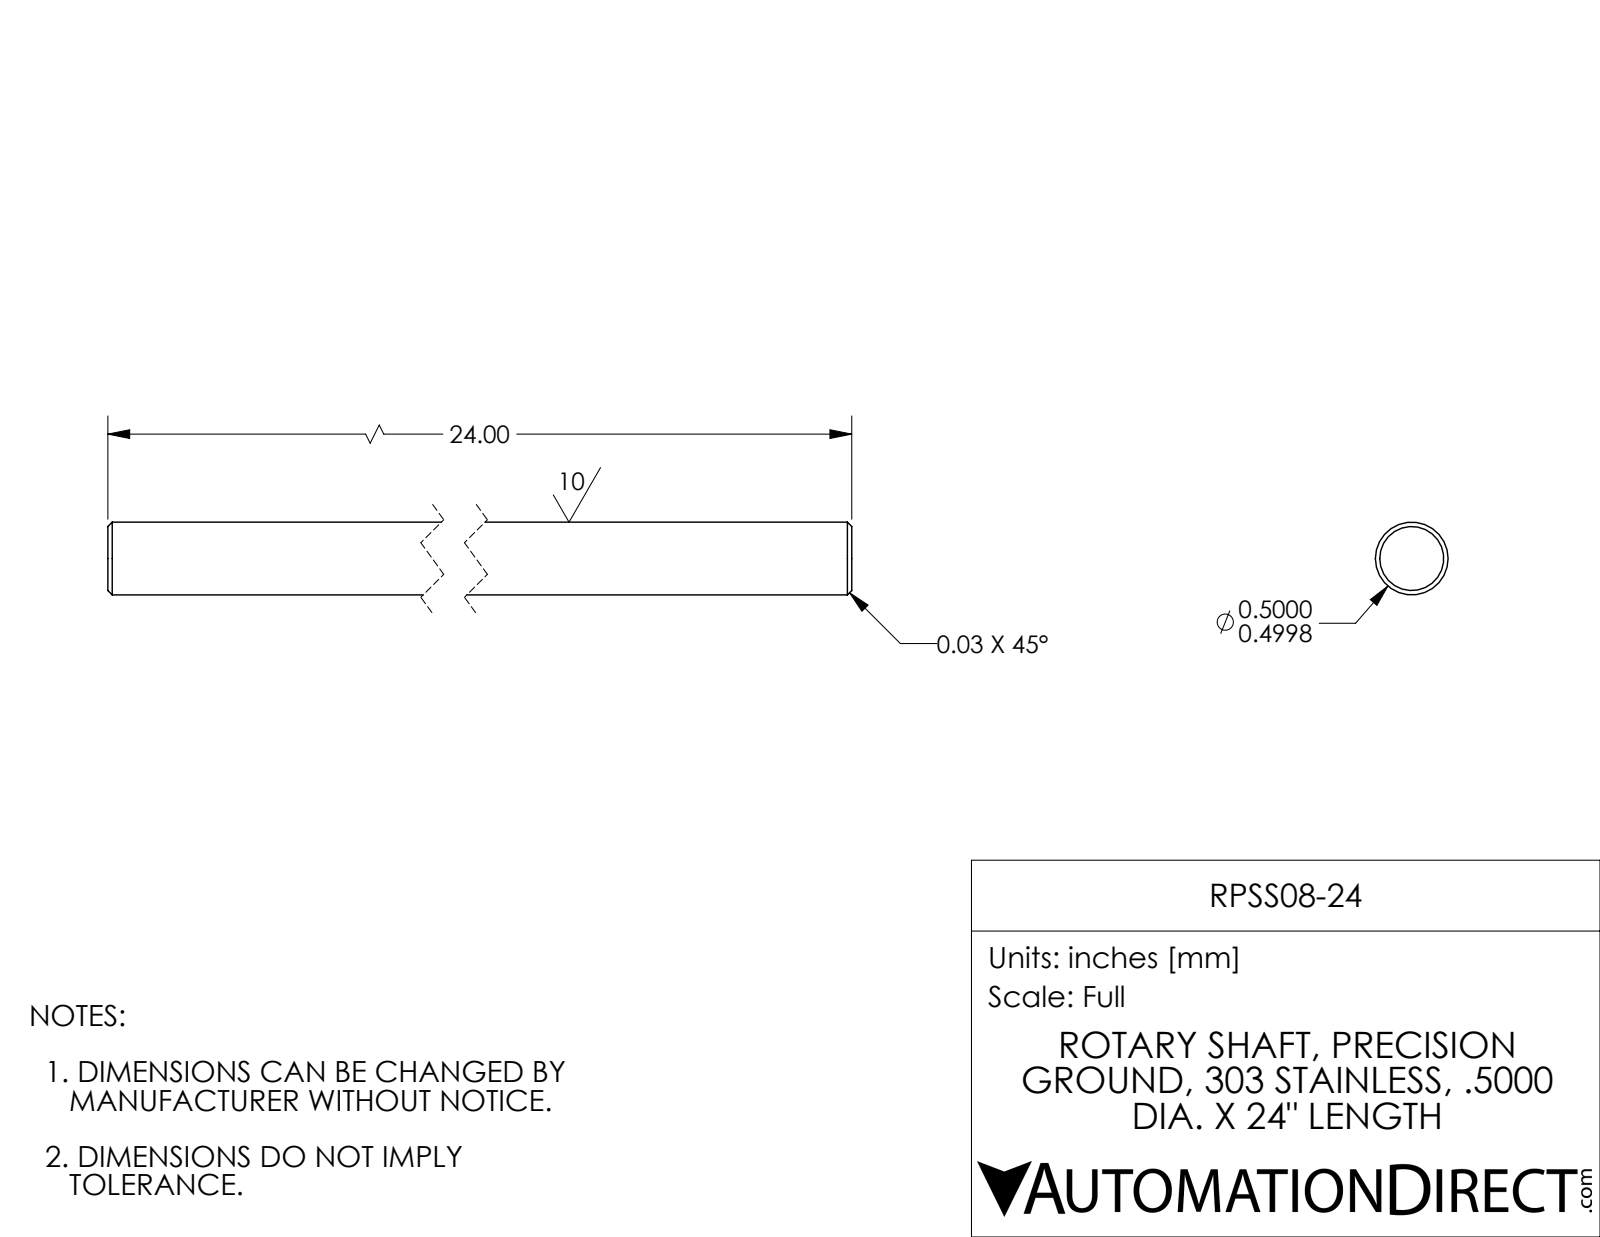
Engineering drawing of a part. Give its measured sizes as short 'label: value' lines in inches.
name: RPSS08-24
written by: SolidWorks 2017 (AUTOMOTIVE_DESIGN)
unit: in
bodies: 1 solid, 8 faces (2 planar, 2 cylindrical, 4 other)
size: 24 × 0.5 × 0.5
volume: 4.711 in³; area: 38.03 in²
bosses: 1× ⌀0.5
face distances: 24
